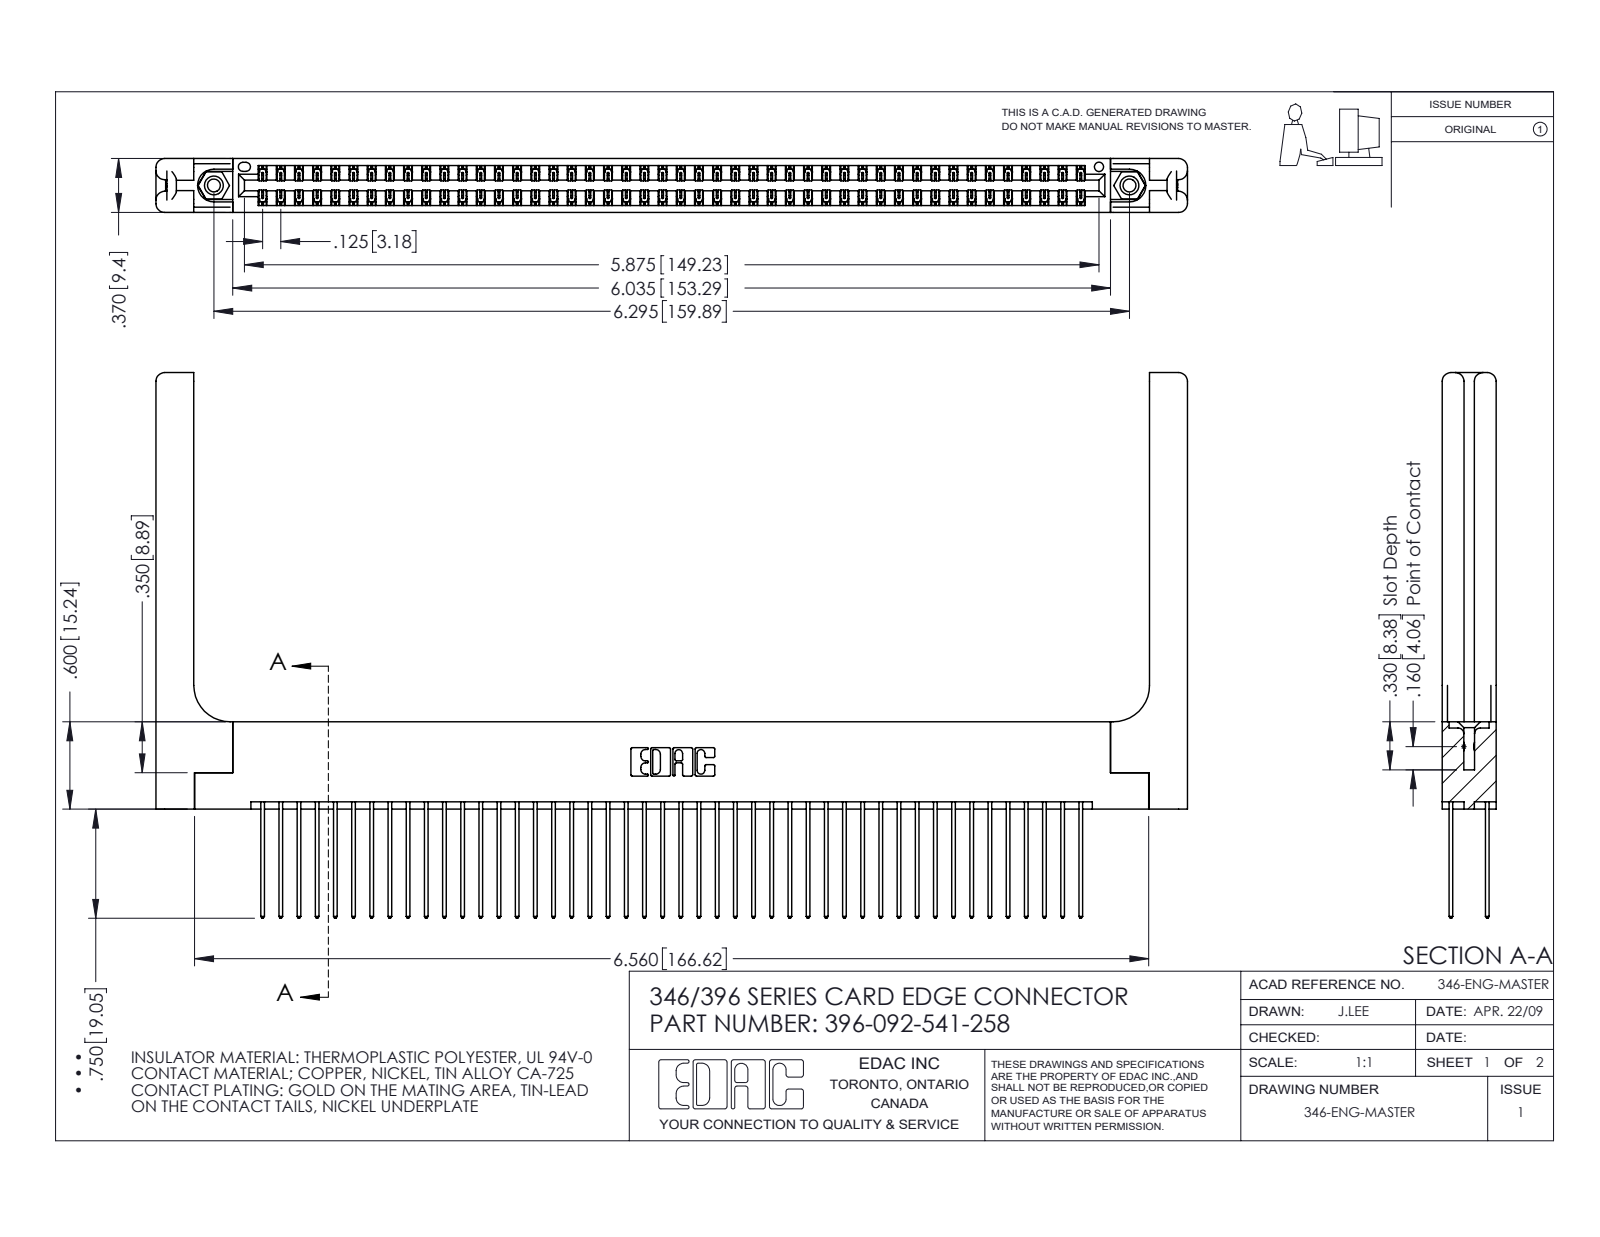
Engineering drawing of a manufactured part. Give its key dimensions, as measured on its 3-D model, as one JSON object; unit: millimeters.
{"part_name": "346 Part_Flush Mounting Lugs - 0.156 Dia-TH; 345-250-001_345-250-001-102; 345-292-001_345-293-141; 396-092-541-258 (+1 more)", "step_written_by": "SolidWorks 2016 (CONFIG_CONTROL_DESIGN)", "units": "millimeters", "bodies": {"solids": 97, "faces": 5162, "planar": 3444, "cylindrical": 1658, "other": 60}, "overall_size": [180.1, 95.3, 9.4], "volume_mm3": 25610, "surface_area_mm2": 32480, "round_holes": [[2.3, 2], [3.2, 2], [4, 2], [1.6, 1]], "round_bosses_or_shafts": [[3.9, 2]], "partial_cylinders_radius": [[0.2, 138], [0.3, 92], [0.3, 22], [1.5, 16], [0.2, 6], [0.8, 6], [0.7, 3], [0.4, 2]], "face_to_face_distances": [1.2, 8.2, 1.8, 9.4, 6.4, 0.6, 7.6, 7, 3.8, 3.8], "hole_center_spacings": [6.2, 154.6, 159.9]}
